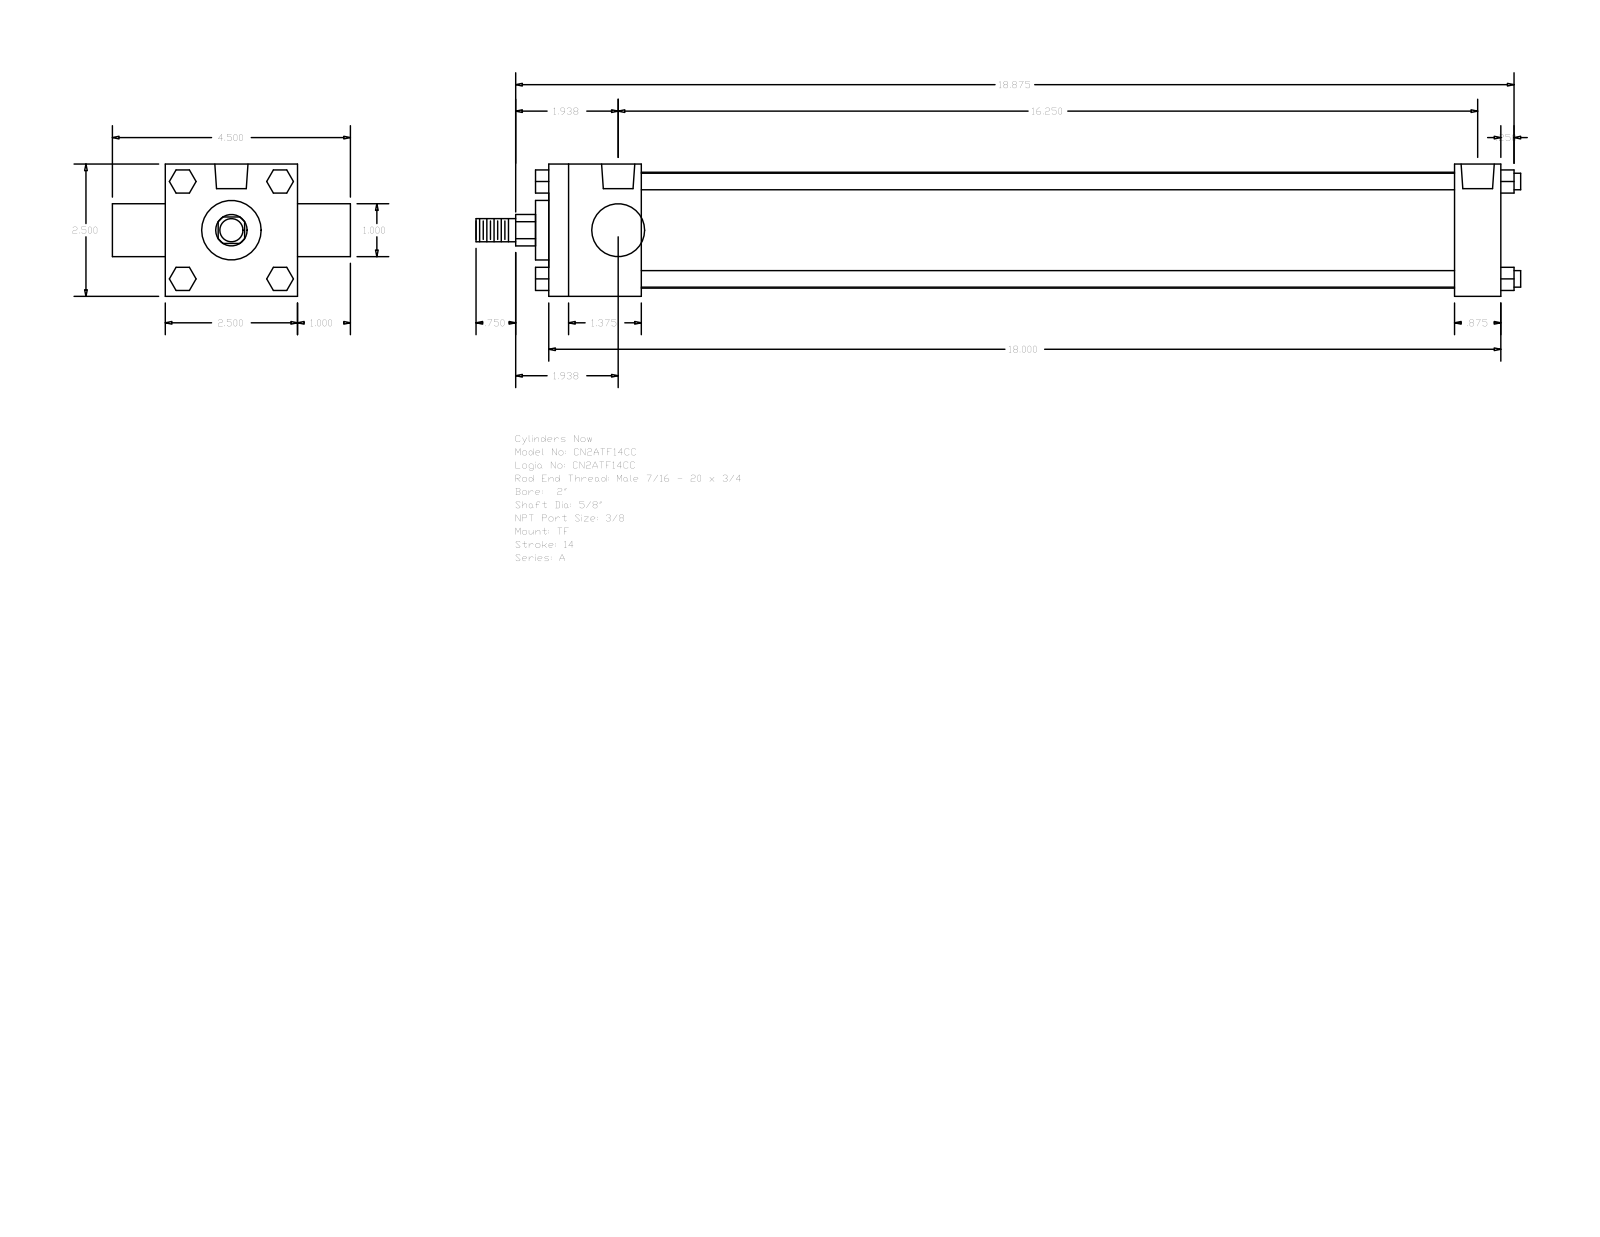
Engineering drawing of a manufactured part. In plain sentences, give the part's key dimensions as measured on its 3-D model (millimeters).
The part is named "A_TF__0200_0.625". Its 3-D file was written by "GSSL Pune (CONFIG_CONTROL_DESIGN)". It is 0 solids with 120 faces: 92 planar, 28 cylindrical and 0 other. Overall it measures 501.65 by 114.3 by 63.5 millimeters. Round holes: 3 of diameter 5.56, 2 of diameter 15.93. Round bosses or shafts: 4 of diameter 7.94, 1 of diameter 55.63, 1 of diameter 28.57, 1 of diameter 25.4, 1 of diameter 15.88, 1 of diameter 11.11. Partial cylindrical surfaces (rounded edges, fillets, slot ends): 1 of radius 7.54. The main face-to-face distances are 63.5, 457.19, 44.45, 434.97, 390.52, 412.74, 22.22, 25.4, 88.9, 50.8. The hole center spacings are 3.97, 3.98, 404.8, 408.77, 408.78, 412.75.
